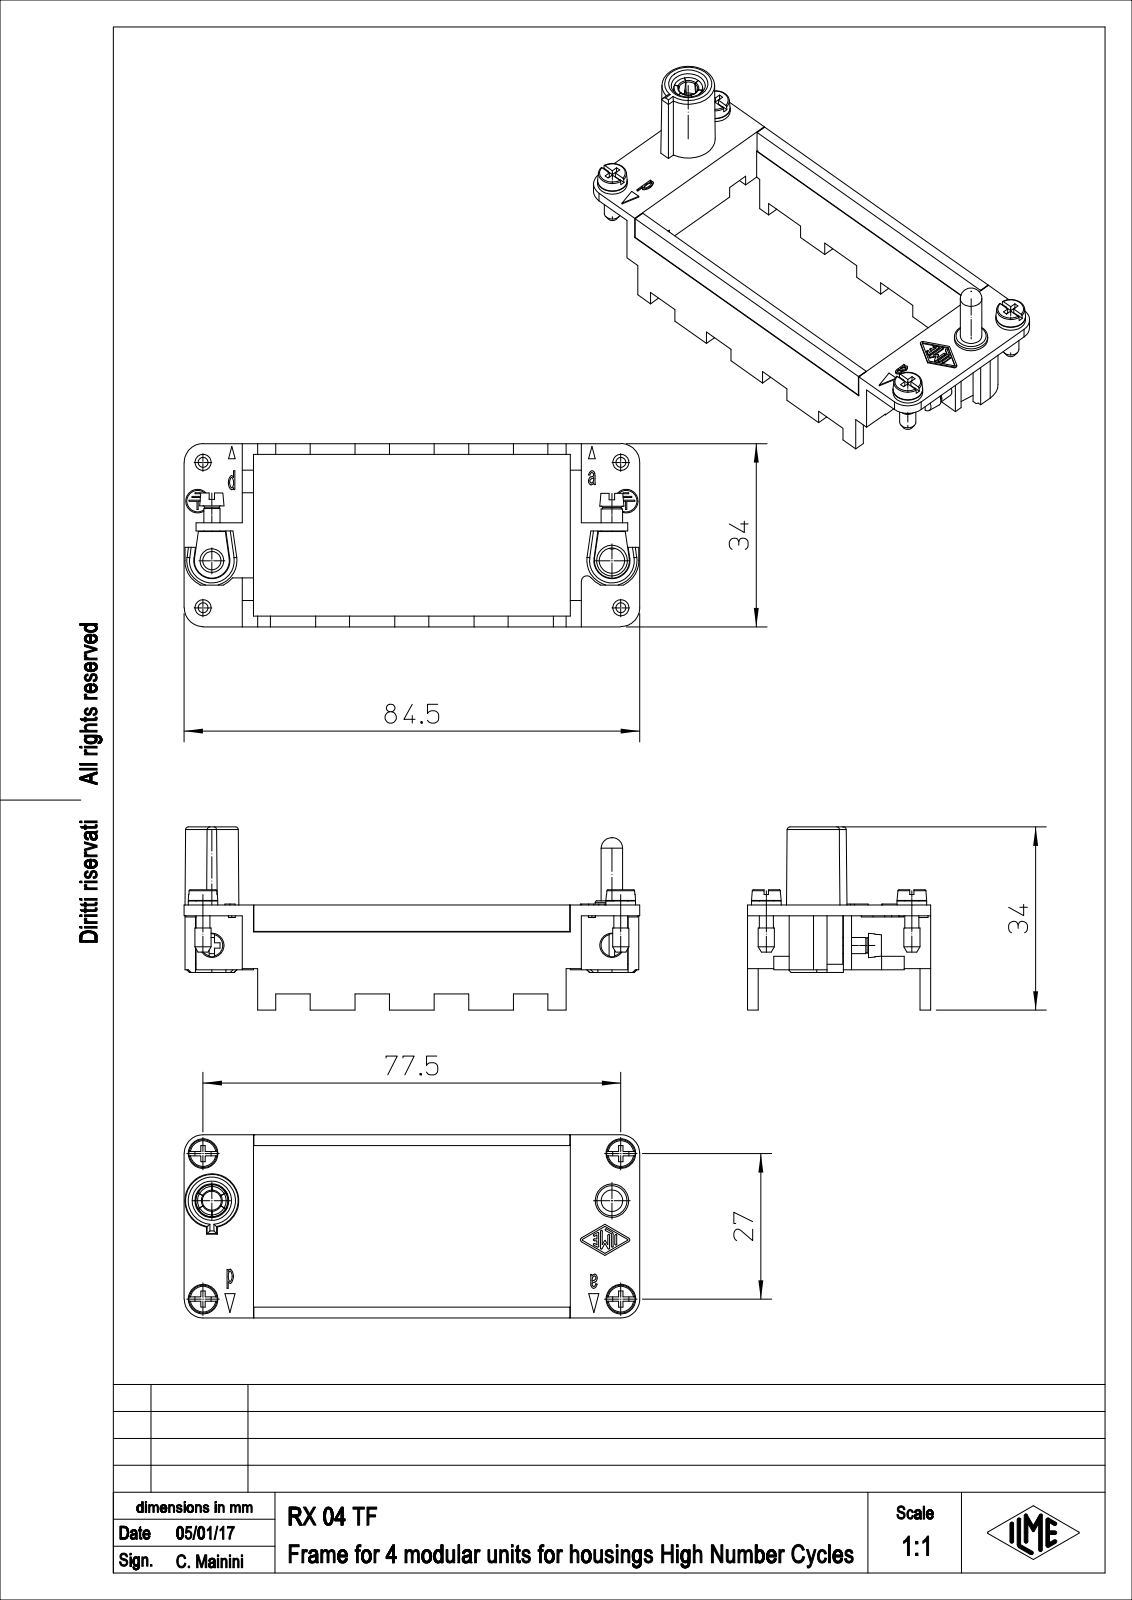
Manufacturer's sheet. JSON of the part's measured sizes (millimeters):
{"part_name": "RX_04_TF", "step_written_by": "PTC Creo Elements/Direct Modeling 19.0E 27-Jun-2016 (C) Parametric Technology GmbH (AUTOMOTIVE_DESIGN)", "units": "millimeters", "bodies": {"solids": 1, "faces": 650, "planar": 405, "cylindrical": 105, "other": 140}, "overall_size": [84.5, 34, 34], "volume_mm3": 10554, "surface_area_mm2": 12159, "round_holes": [[4, 2], [2.5, 1], [3.3, 1], [3.4, 1], [4.2, 1], [4.7, 1], [6.3, 1]], "round_bosses_or_shafts": [[3, 5], [5.5, 4], [2.6, 4], [4.4, 2], [4, 2], [6.2, 1], [6, 1], [3.5, 1]], "partial_cylinders_radius": [[0.17, 11], [3.5, 4], [0.5, 3], [0.13, 2], [0.41, 2], [3.25, 2], [3.35, 2], [5, 2]], "face_to_face_distances": [2, 32, 34, 30, 2.05, 60.85, 58.8, 12.7, 62.9, 12.85], "hole_center_spacings": [74.2, 11.37, 11.38, 77.64, 77.65, 79.51]}
